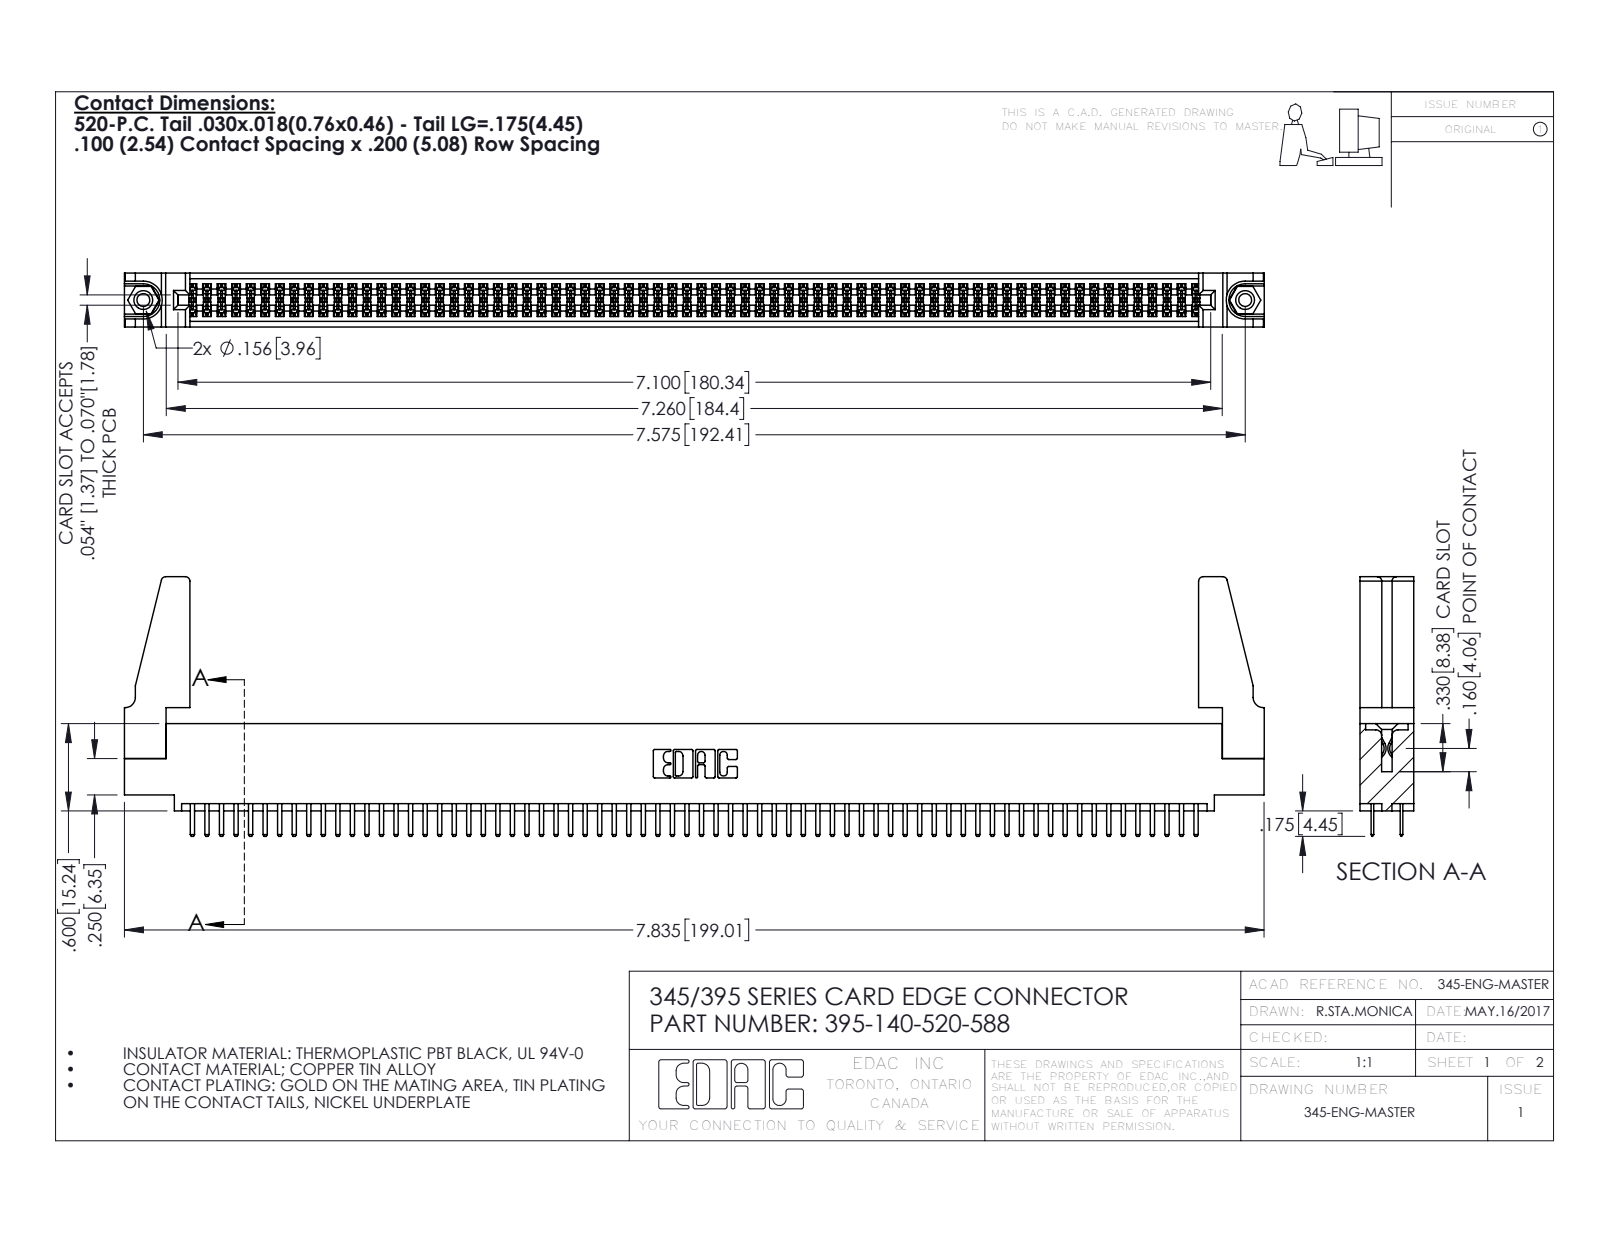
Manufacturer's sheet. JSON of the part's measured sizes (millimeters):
{"part_name": "345-250-001_345-250-001-102; 345-292-001_345-293-120; 345 Part_0.110 Offset - 0.156 Dia-TH; 395-140-520-588 (+1 more)", "step_written_by": "SolidWorks 2016 (CONFIG_CONTROL_DESIGN)", "units": "millimeters", "bodies": {"solids": 145, "faces": 7814, "planar": 5056, "cylindrical": 2742, "other": 16}, "overall_size": [199, 45.3, 9.4], "volume_mm3": 22710, "surface_area_mm2": 32390, "round_holes": [[2.3, 2], [3.2, 2], [4, 2], [1.6, 1]], "round_bosses_or_shafts": [[3.9, 2]], "partial_cylinders_radius": [[0.2, 210], [0.3, 144], [0.3, 22], [0.8, 8], [0.2, 6], [0.8, 6], [0.7, 3], [0.4, 2]], "face_to_face_distances": [1.8, 7.6, 9.4, 5.1, 2.5, 6.9, 0.6, 5.7, 0.6, 1.8], "hole_center_spacings": [6.9, 186.4, 192.4]}
